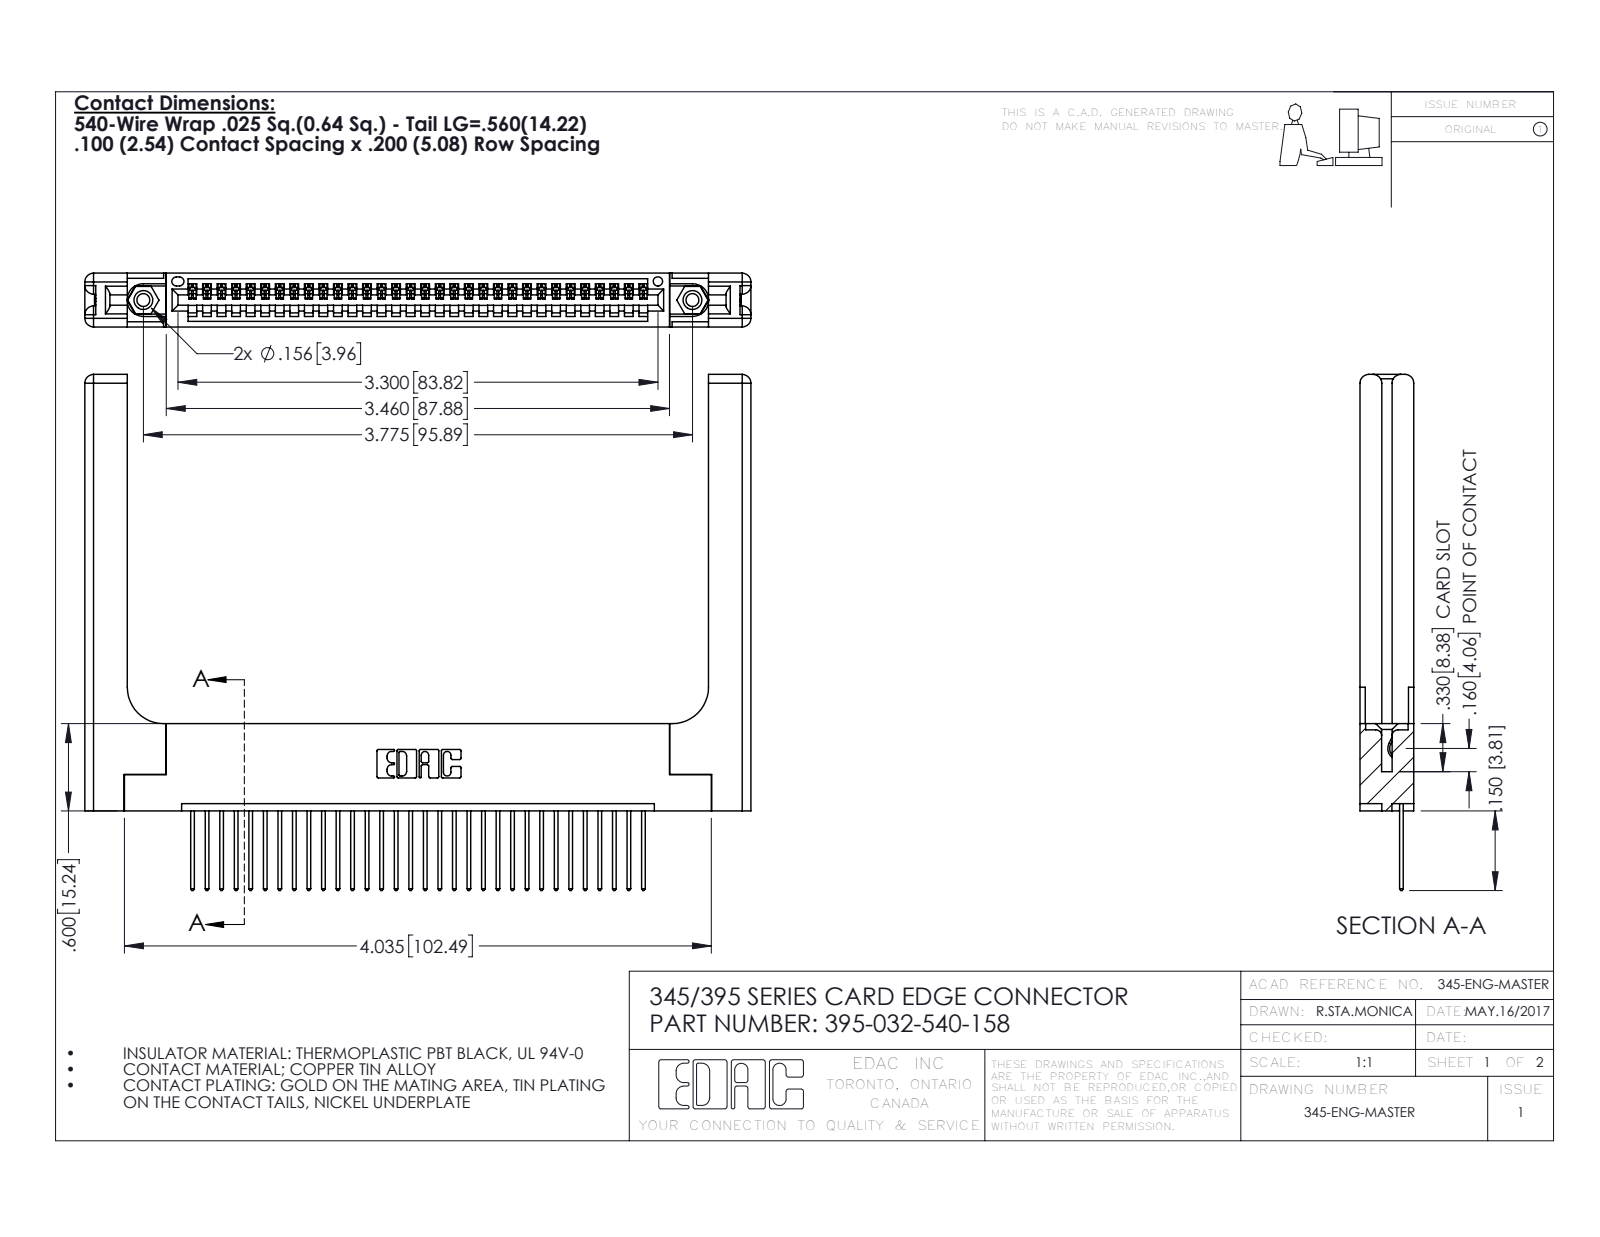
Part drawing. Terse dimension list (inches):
name: 345 Part_Flush Mounting Lugs - 0.156 Dia-TH; 345-220-058_345-220-058; 395-032-540-158; 345-250-001_345-250-001-102 (+1 more)
written by: SolidWorks 2016 (CONFIG_CONTROL_DESIGN)
unit: in
bodies: 37 solids, 2238 faces (1508 planar, 670 cylindrical, 60 other)
size: 4.579 × 3.547 × 0.37
volume: 1.191 in³; area: 31.17 in²
holes: 2× ⌀0.089, 2× ⌀0.125, 2× ⌀0.156, 1× ⌀0.064
bosses: 2× ⌀0.155
rounds: 64× R0.006, 64× R0.01, 22× R0.01, 16× R0.06, 6× R0.007, 6× R0.031, 3× R0.026, 2× R0.03
face distances: 0.37, 0.072, 0.298, 0.2, 0.098, 0.272, 0.025, 0.148, 0.15, 0.077
hole spacings: 0.27, 3.54, 3.775
